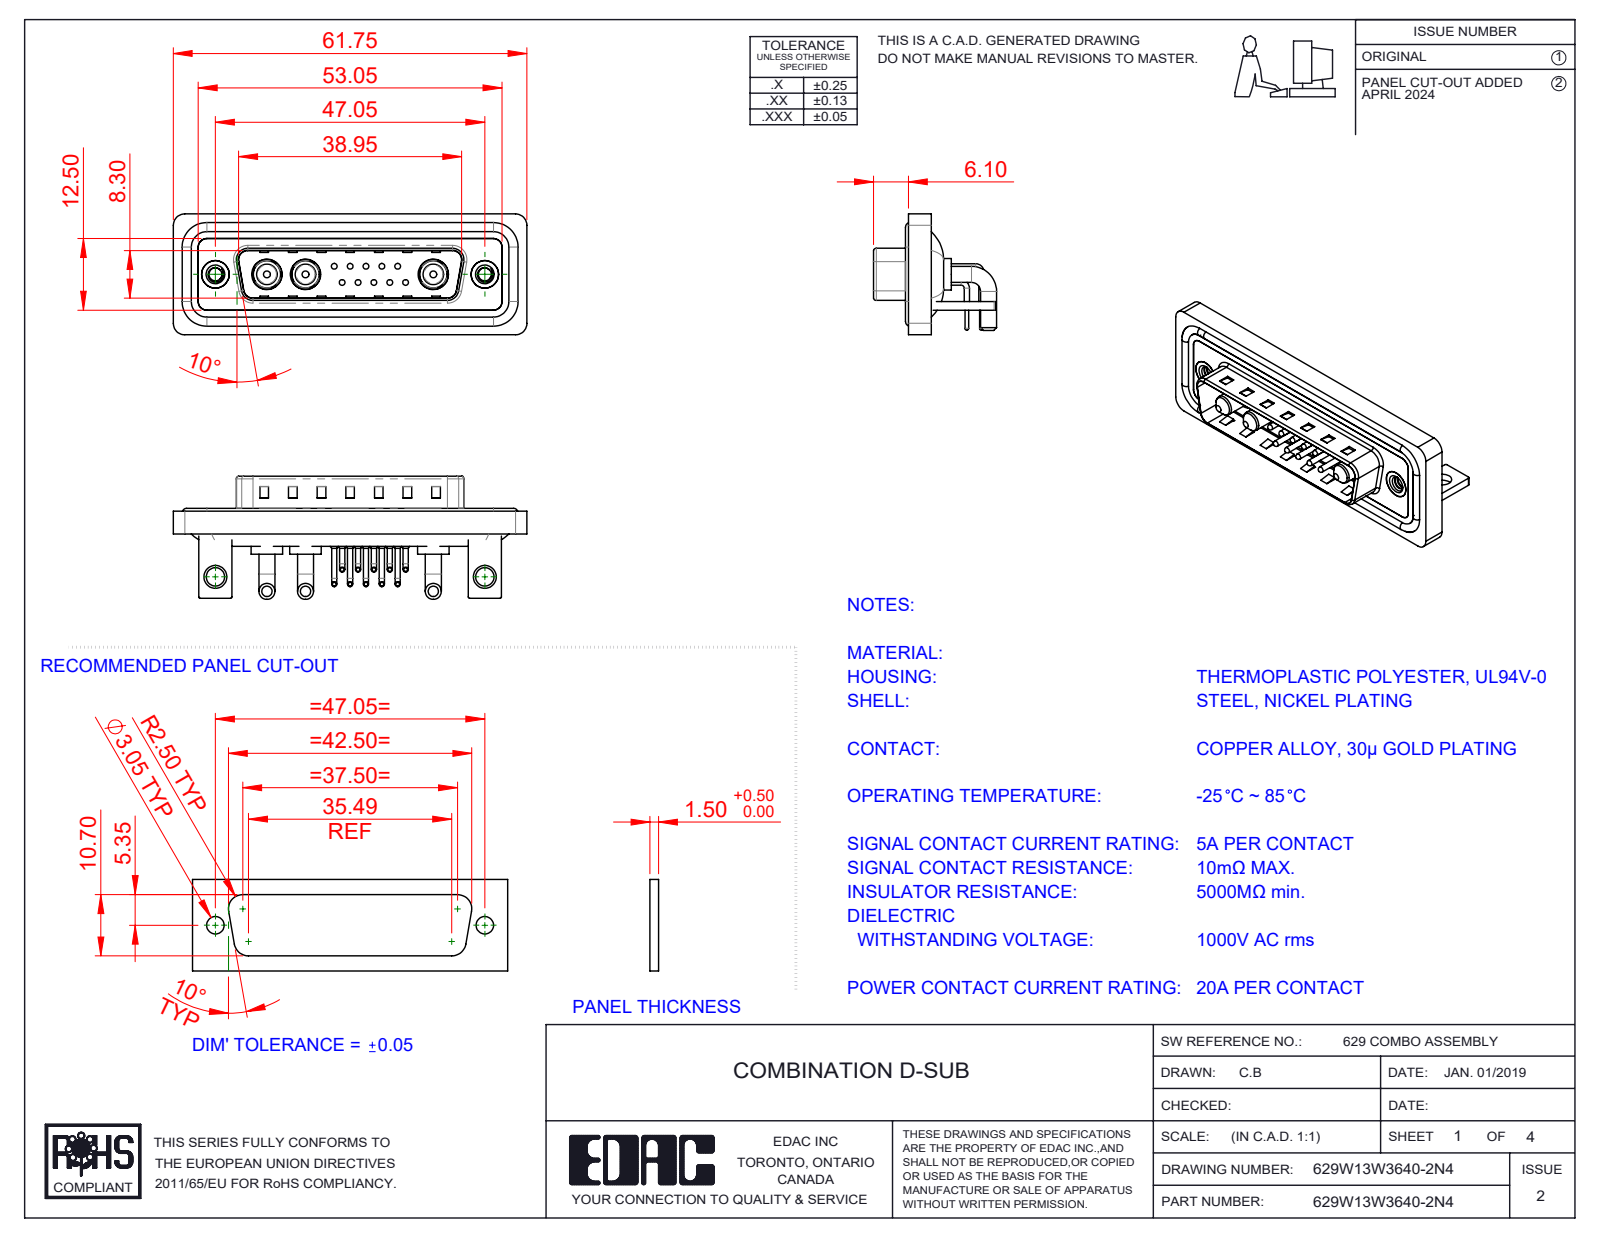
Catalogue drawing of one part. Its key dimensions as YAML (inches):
part_name: "629Combo Stabilizer Bracket; 629Combo Threaded Rivet_3; 629Combo Shell Front_25 Contacts; 629Combo Contact Row 2 (+6 more)"
step_written_by: "SolidWorks 2023 (CONFIG_CONTROL_DESIGN)"
units: inches
bodies: {solids: 25, faces: 1752, planar: 899, cylindrical: 629, other: 224}
overall_size: [2.431, 0.846, 0.831]
volume: 0.481
surface_area: 20.28
round_holes:
  - {diameter: 0.03, count: 10}
  - {diameter: 0.063, count: 10}
  - {diameter: 0.079, count: 10}
  - {diameter: 0.191, count: 3}
  - {diameter: 0.209, count: 3}
  - {diameter: 0.089, count: 2}
  - {diameter: 0.126, count: 2}
  - {diameter: 0.157, count: 2}
  - {diameter: 0.189, count: 2}
  - {diameter: 0.197, count: 2}
round_bosses_or_shafts:
  - {diameter: 0.035, count: 20}
  - {diameter: 0.059, count: 10}
  - {diameter: 0.039, count: 10}
  - {diameter: 0.026, count: 10}
  - {diameter: 0.11, count: 6}
  - {diameter: 0.063, count: 4}
  - {diameter: 0.217, count: 3}
  - {diameter: 0.205, count: 3}
partial_cylinders:
  - {radius: 0.079, count: 19}
  - {radius: 0.059, count: 18}
  - {radius: 0.01, count: 16}
  - {radius: 0.04, count: 10}
  - {radius: 0.02, count: 9}
  - {radius: 0.063, count: 8}
  - {radius: 0.024, count: 4}
  - {radius: 0.026, count: 4}
face_to_face_distances: [0.016, 0.031, 0.059, 0.114, 0.083, 0.043, 0.161, 0.063, 0.146, 0.177]
hole_center_spacings: [0.124, 0.109, 0.198, 0.218, 0.295, 0.198, 0.327, 0.398]
